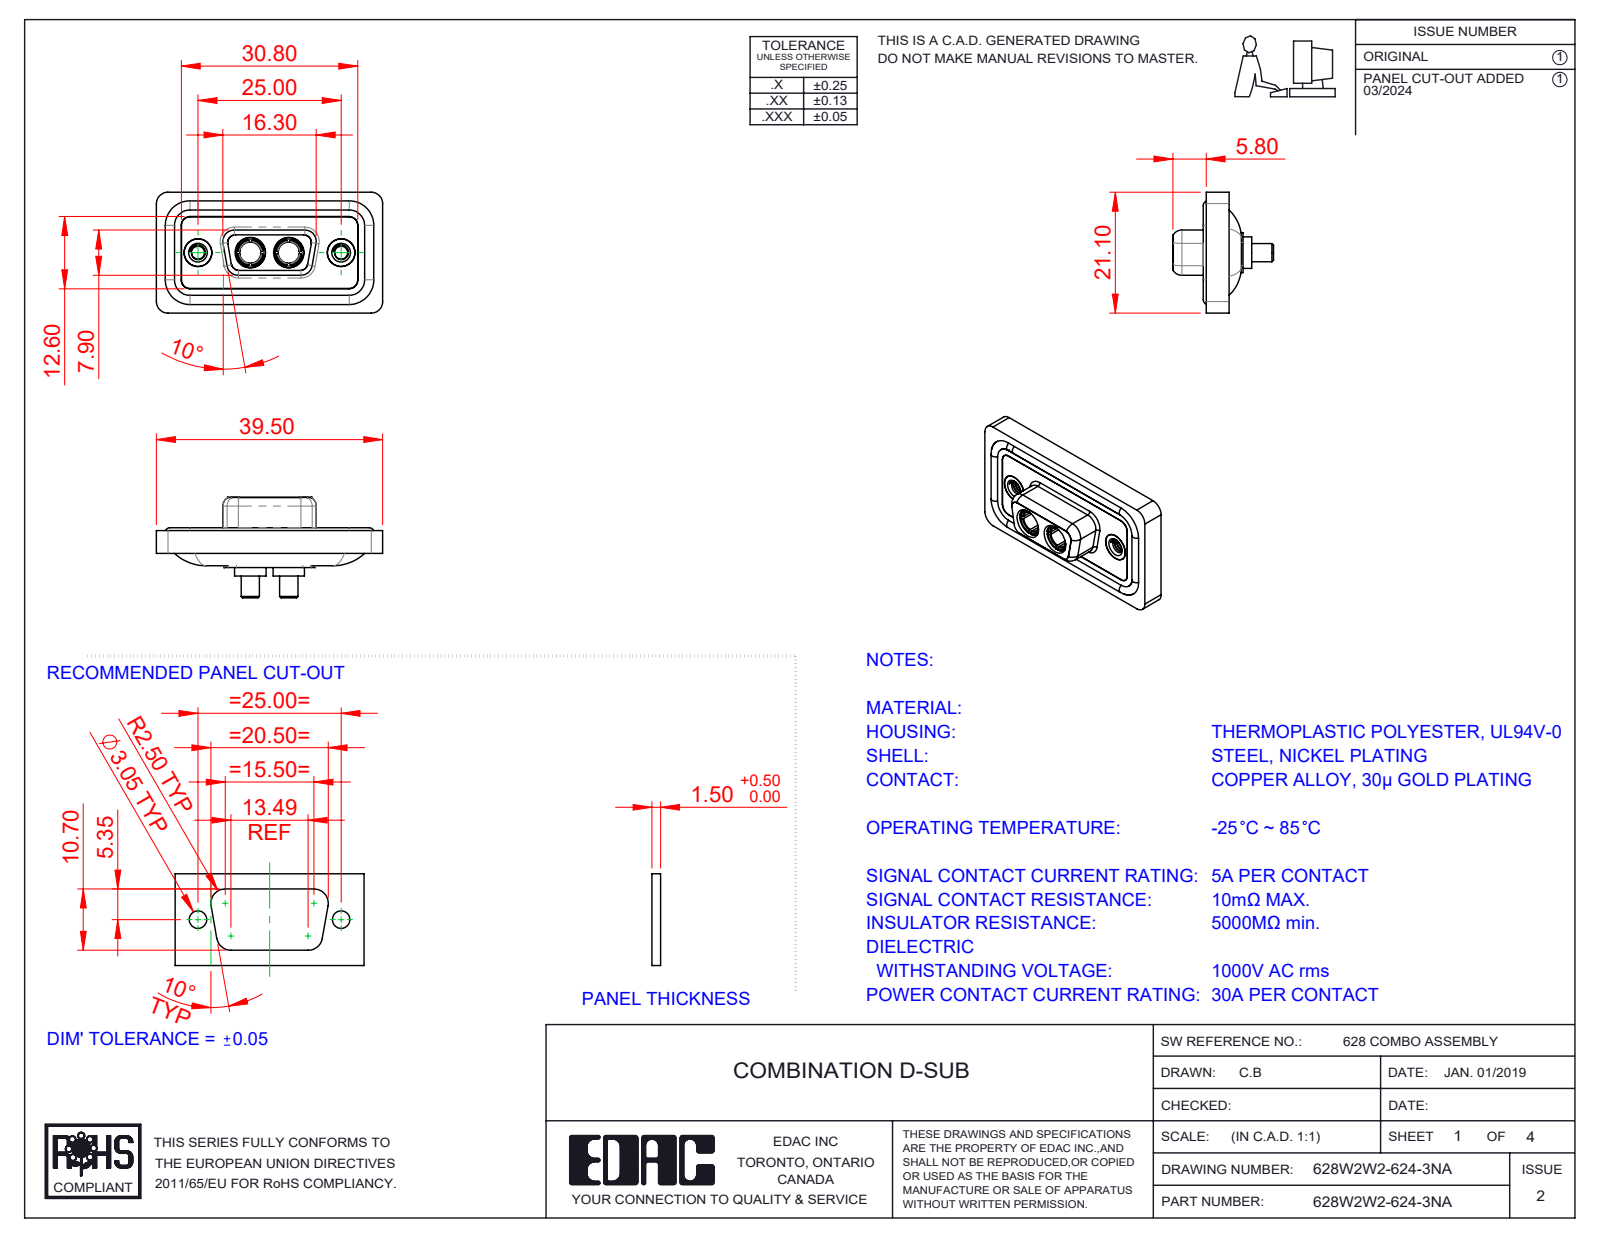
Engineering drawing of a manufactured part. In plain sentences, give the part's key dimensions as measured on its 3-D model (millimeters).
The part is named "628Combo Shell Rear_09 Contacts; 628Combo Housing_2W2; 628Combo Shell Front_09 Contacts; Power Socket_30A S (+3 more)". Its 3-D file was written by "SolidWorks 2023 (CONFIG_CONTROL_DESIGN)". It is 11 solids with 532 faces: 163 planar, 236 cylindrical and 133 other. Overall it measures 39.5 by 21.1 by 17.55 millimeters. Its volume is 4 729 cubic millimeters and its surface area 7 643 square millimeters. Round holes: 4 of diameter 4.85, 2 of diameter 2.26, 2 of diameter 3.7, 2 of diameter 4, 2 of diameter 4.05, 2 of diameter 5, 2 of diameter 5.3. Round bosses or shafts: 4 of diameter 1.6, 2 of diameter 5.5, 2 of diameter 5.2, 2 of diameter 4.96, 2 of diameter 4.95, 2 of diameter 4.8, 2 of diameter 4.75, 2 of diameter 3.75. Partial cylindrical surfaces (rounded edges, fillets, slot ends): 22 of radius 1.5, 18 of radius 2, 8 of radius 1.35, 8 of radius 1.6, 4 of radius 0.25, 4 of radius 0.5, 4 of radius 0.6, 4 of radius 0.65. The main face-to-face distances are 0.4, 1.8, 1.1, 2.9, 0.5, 1.6, 5.65, 7.45, 1.5, 5.35. The hole center spacings are 9.14, 15.86, 6.72, 25.
